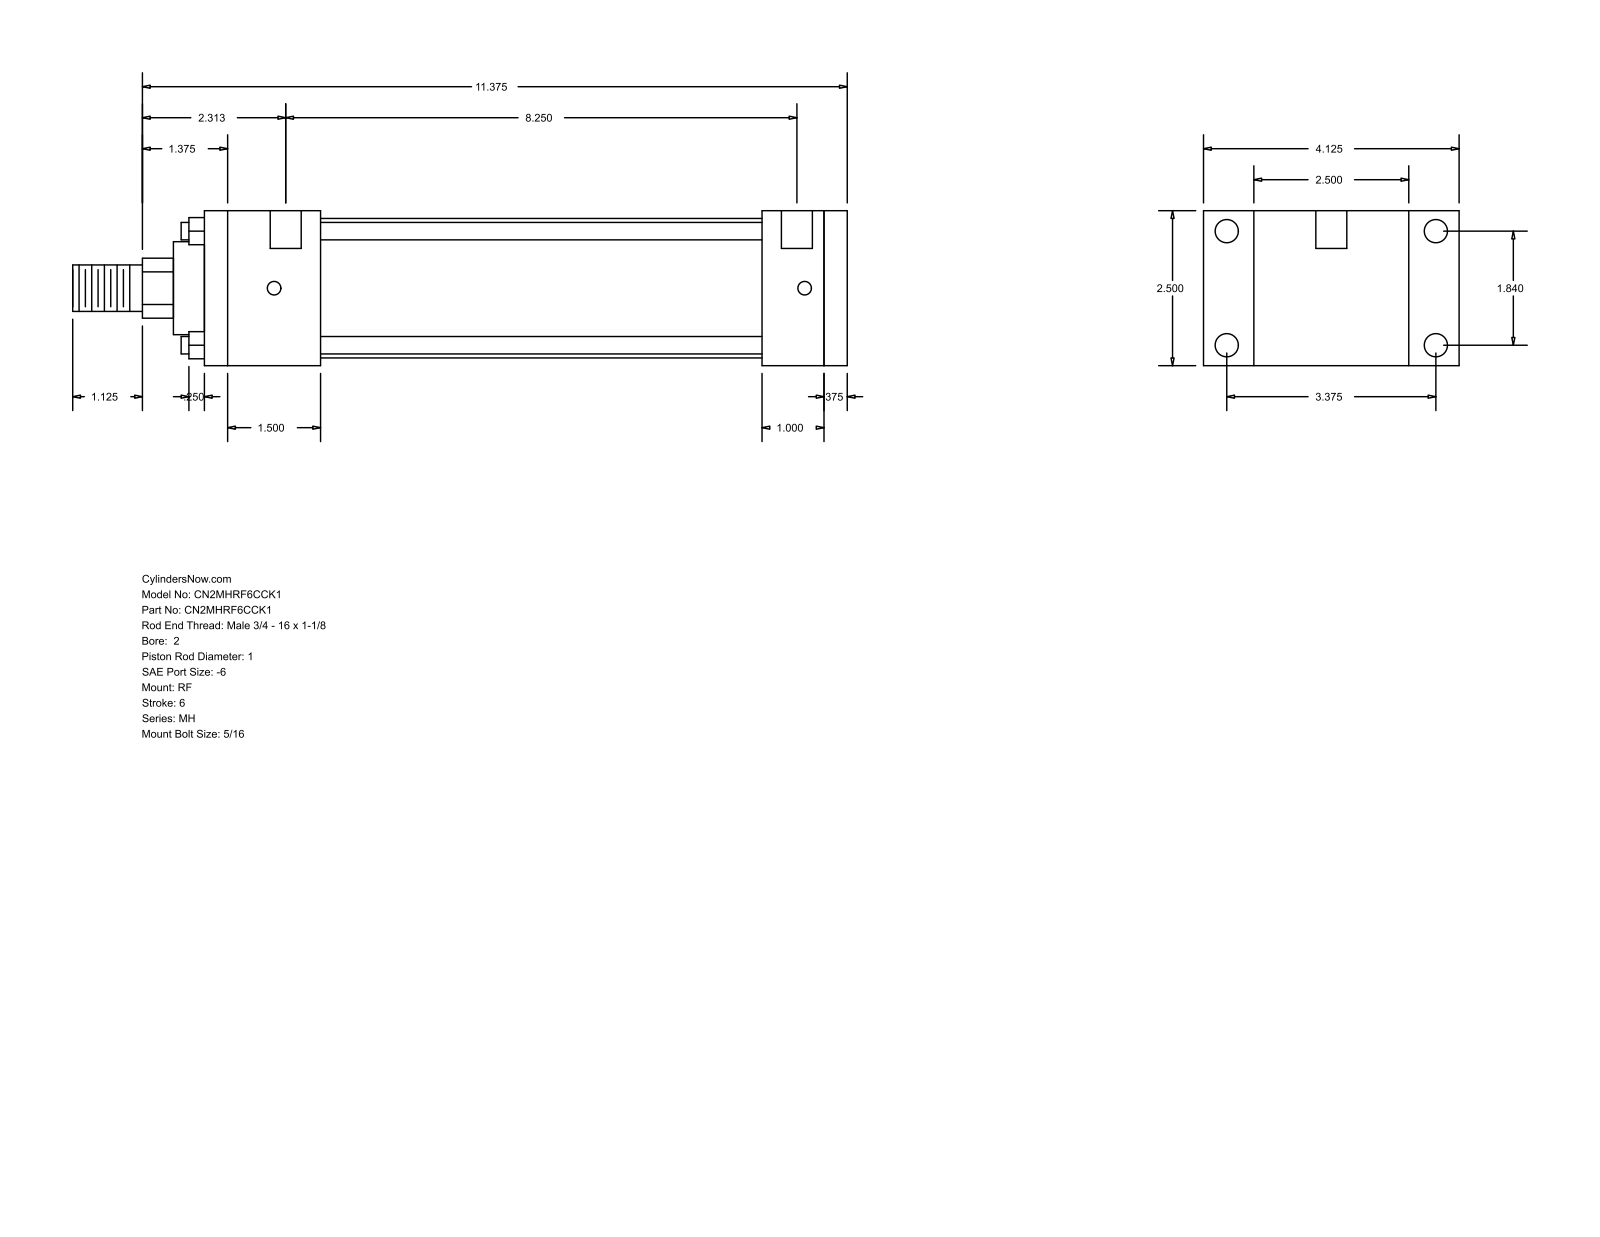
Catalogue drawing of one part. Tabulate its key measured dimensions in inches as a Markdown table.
| quantity | value |
| --- | --- |
| part name | MH_RF__0200_1 |
| STEP written by | GSSL Pune (CONFIG_CONTROL_DESIGN) |
| units | inches |
| bodies | 0 solids, 92 faces (64 planar, 28 cylindrical, 0 other) |
| overall size | 12.5 × 4.125 × 2.5 |
| round holes (diameter × count) | 0.219 × 4, 0.375 × 4, 0.5 × 2 |
| round bosses / shafts (diameter × count) | 0.281 × 4, 2.25 × 1, 1.5 × 1, 1 × 1, 0.75 × 1 |
| partial cylindrical surfaces (radius × count) | 0.484 × 1 |
| main face-to-face distances | 2.5, 10.375, 10, 0.375, 0.813, 1, 1.875, 9, 7.125, 8.125 |
| hole center spacings | 1.84, 3.375, 3.844, 8.562, 0.125, 0.187, 8.25, 8.375 |
